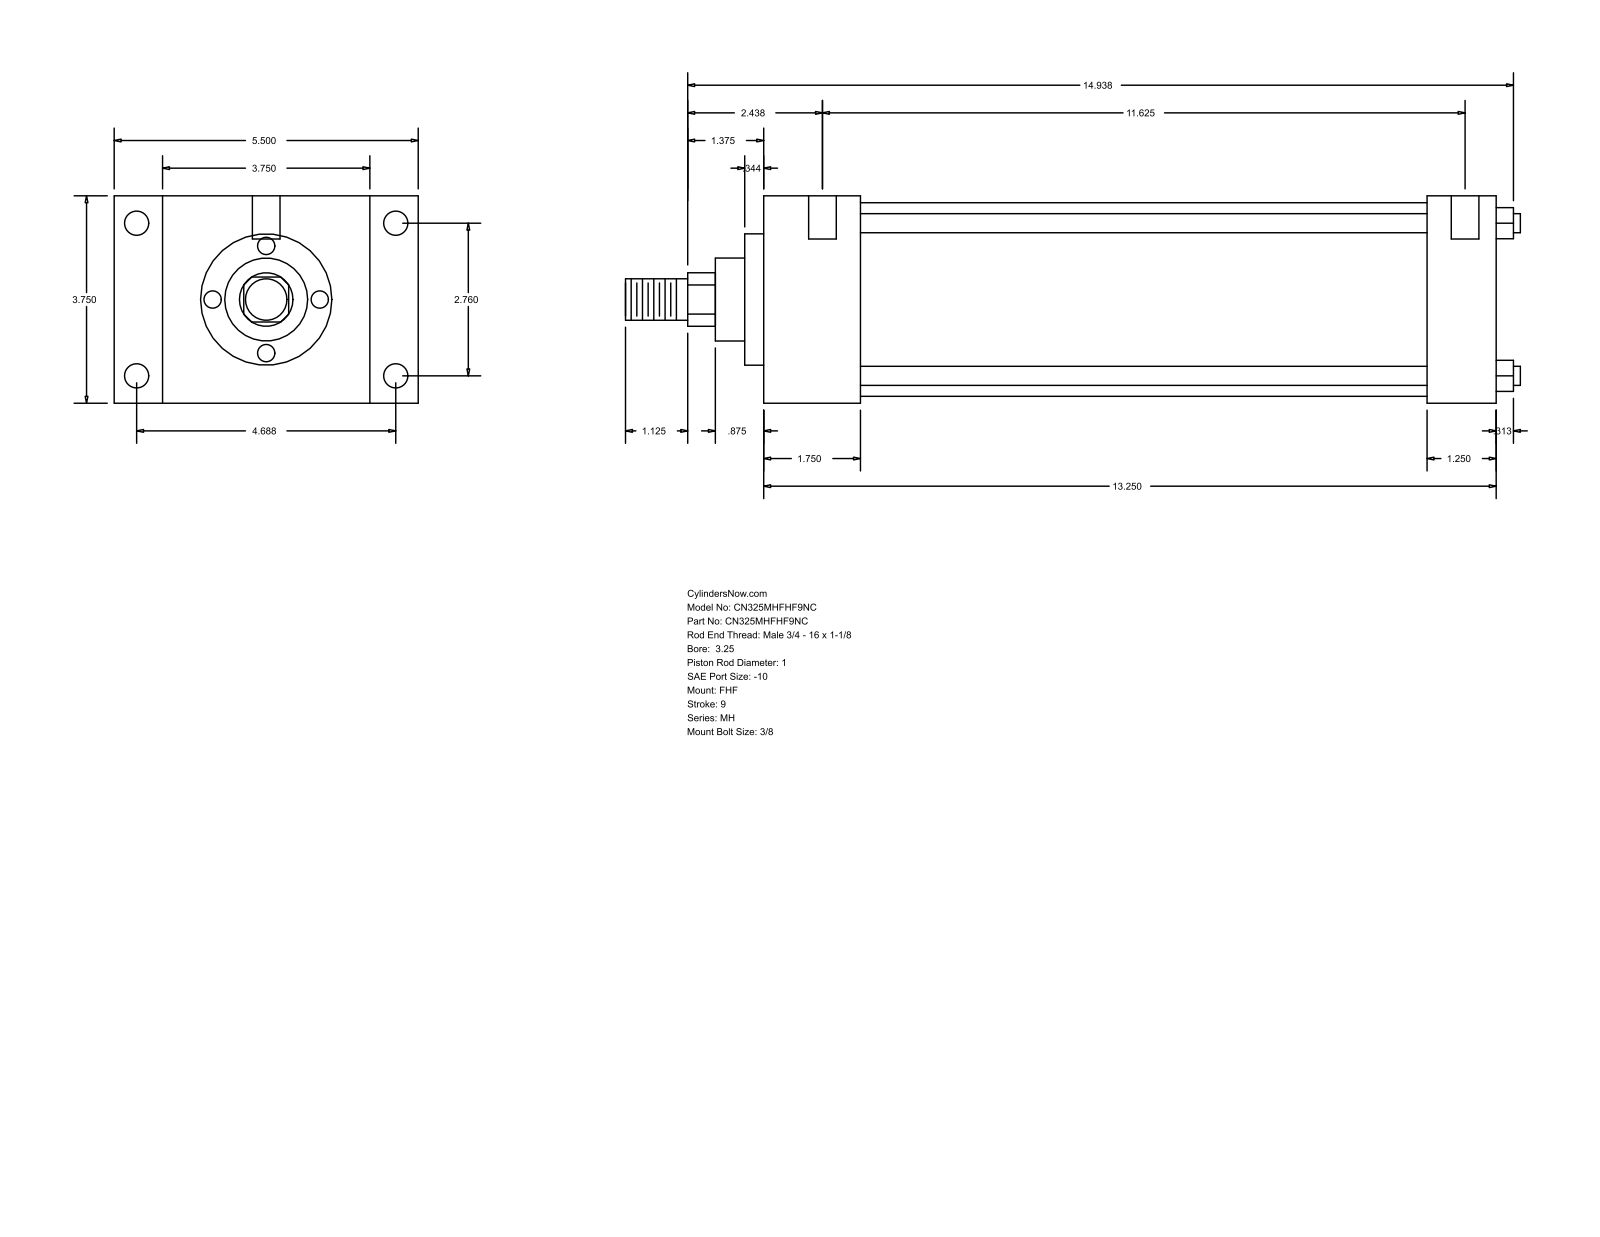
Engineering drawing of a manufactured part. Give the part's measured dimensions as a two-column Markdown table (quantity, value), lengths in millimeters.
| quantity | value |
| --- | --- |
| part name | MH_FHF__0325_1 |
| STEP written by | GSSL Pune (CONFIG_CONTROL_DESIGN) |
| units | millimeters |
| bodies | 0 solids, 90 faces (61 planar, 29 cylindrical, 0 other) |
| overall size | 411.16 × 139.7 × 95.25 |
| round holes (diameter × count) | 5.56 × 4, 11.13 × 4, 12.7 × 2 |
| round bosses / shafts (diameter × count) | 8.76 × 4, 88.9 × 1, 60.33 × 1, 38.1 × 1, 25.4 × 1, 19.05 × 1 |
| partial cylindrical surfaces (radius × count) | 12.29 × 1 |
| main face-to-face distances | 95.24, 336.56, 44.46, 292.1, 22.23, 117.47, 139.7, 304.81, 260.35, 31.75 |
| hole center spacings | 70.1, 119.06, 138.16, 301.62, 1.58, 4.76, 295.28, 296.86 |
